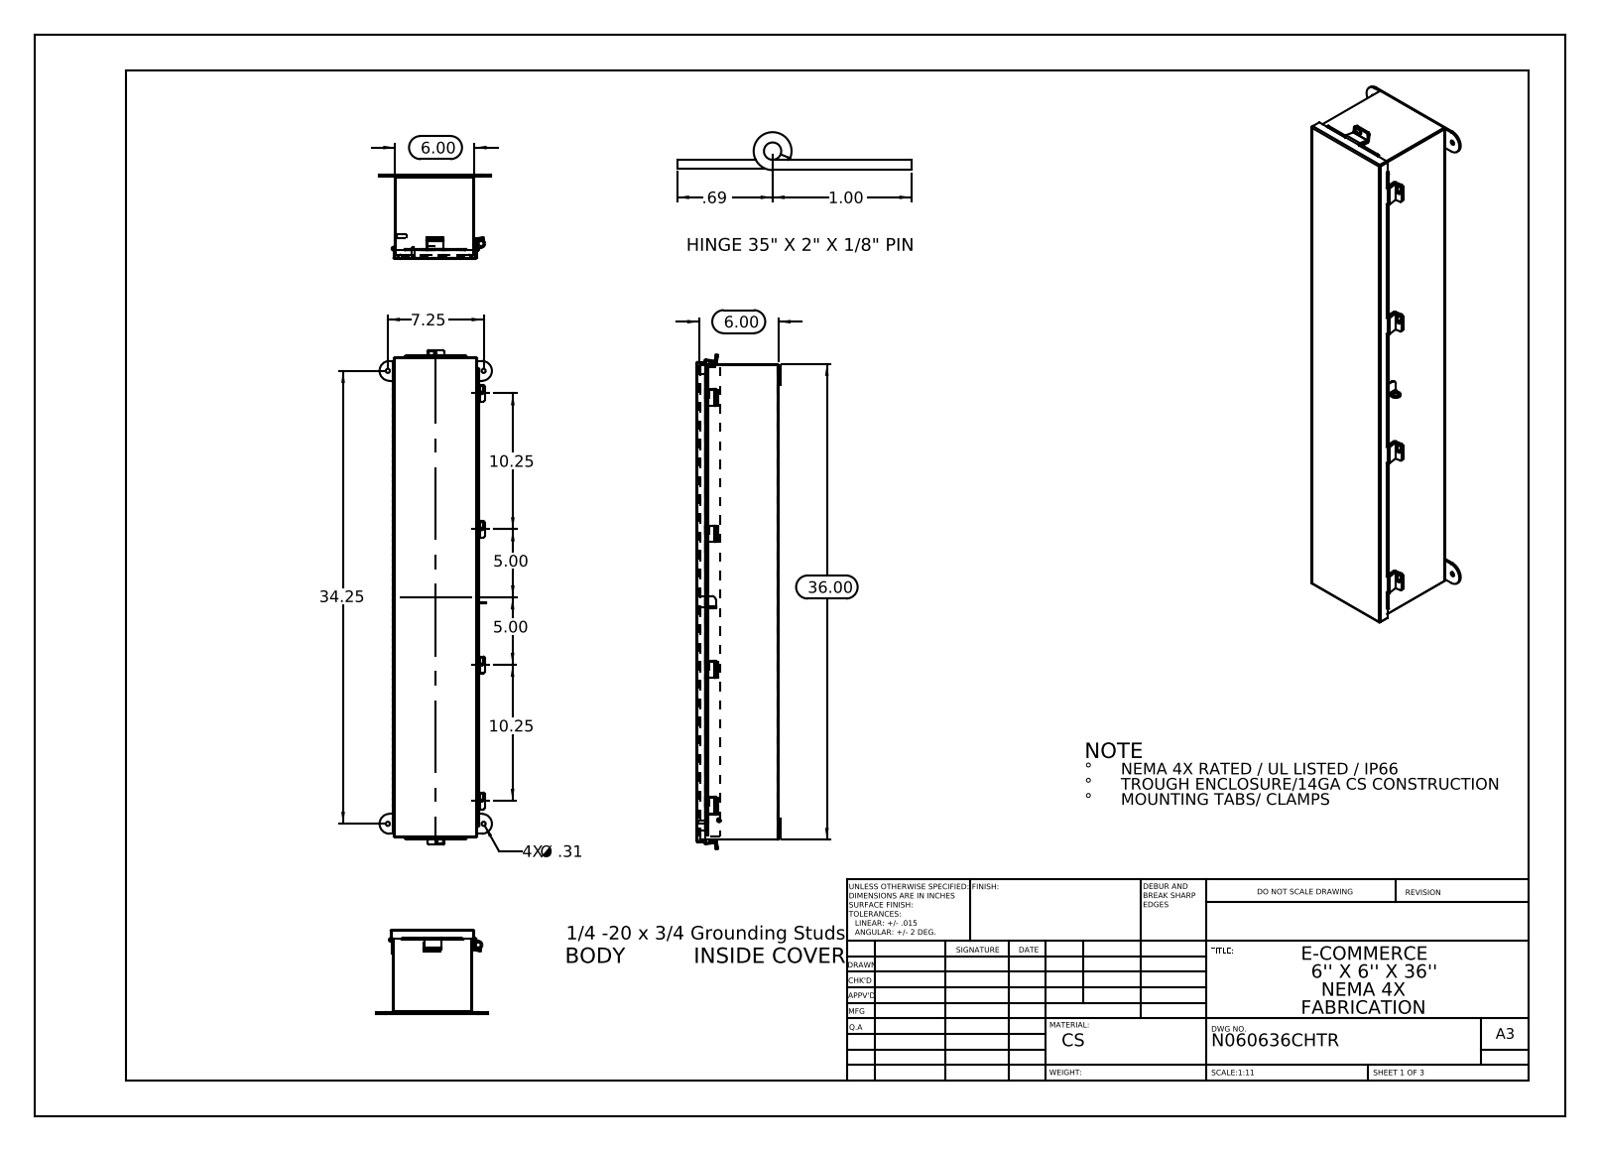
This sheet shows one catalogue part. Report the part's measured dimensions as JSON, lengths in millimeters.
{"part_name": "N060636SSCHTR Hinge Body Side; N060636SSCHTR JIC Enclosure Template; N060636SSCHTR HW-CD-S-25020-034; HW-CLH-JH-20154 (+8 more)", "step_written_by": "SolidWorks 2013 (CONFIG_CONTROL_DESIGN)", "units": "millimeters", "bodies": {"solids": 23, "faces": 1160, "planar": 705, "cylindrical": 435, "other": 20}, "overall_size": [950.1, 215.9, 161], "volume_mm3": 1407000, "surface_area_mm2": 1492000, "round_holes": [[6.4, 6], [8, 4], [3.2, 1], [9.5, 1]], "round_bosses_or_shafts": [[8, 2], [6, 2], [6.9, 1], [6.4, 1]], "partial_cylinders_radius": [[3.2, 22], [0.2, 12], [3.4, 12], [0.3, 10], [2.2, 10], [2.1, 6], [2.5, 6], [19.1, 4]], "face_to_face_distances": [1.9, 150.5, 155.7, 152.4, 148.6, 157.6, 153.7, 3.8, 154.3, 1.9], "hole_center_spacings": [184.2, 261.3, 522.3, 870, 889.2, 168.6, 261, 783.6]}
